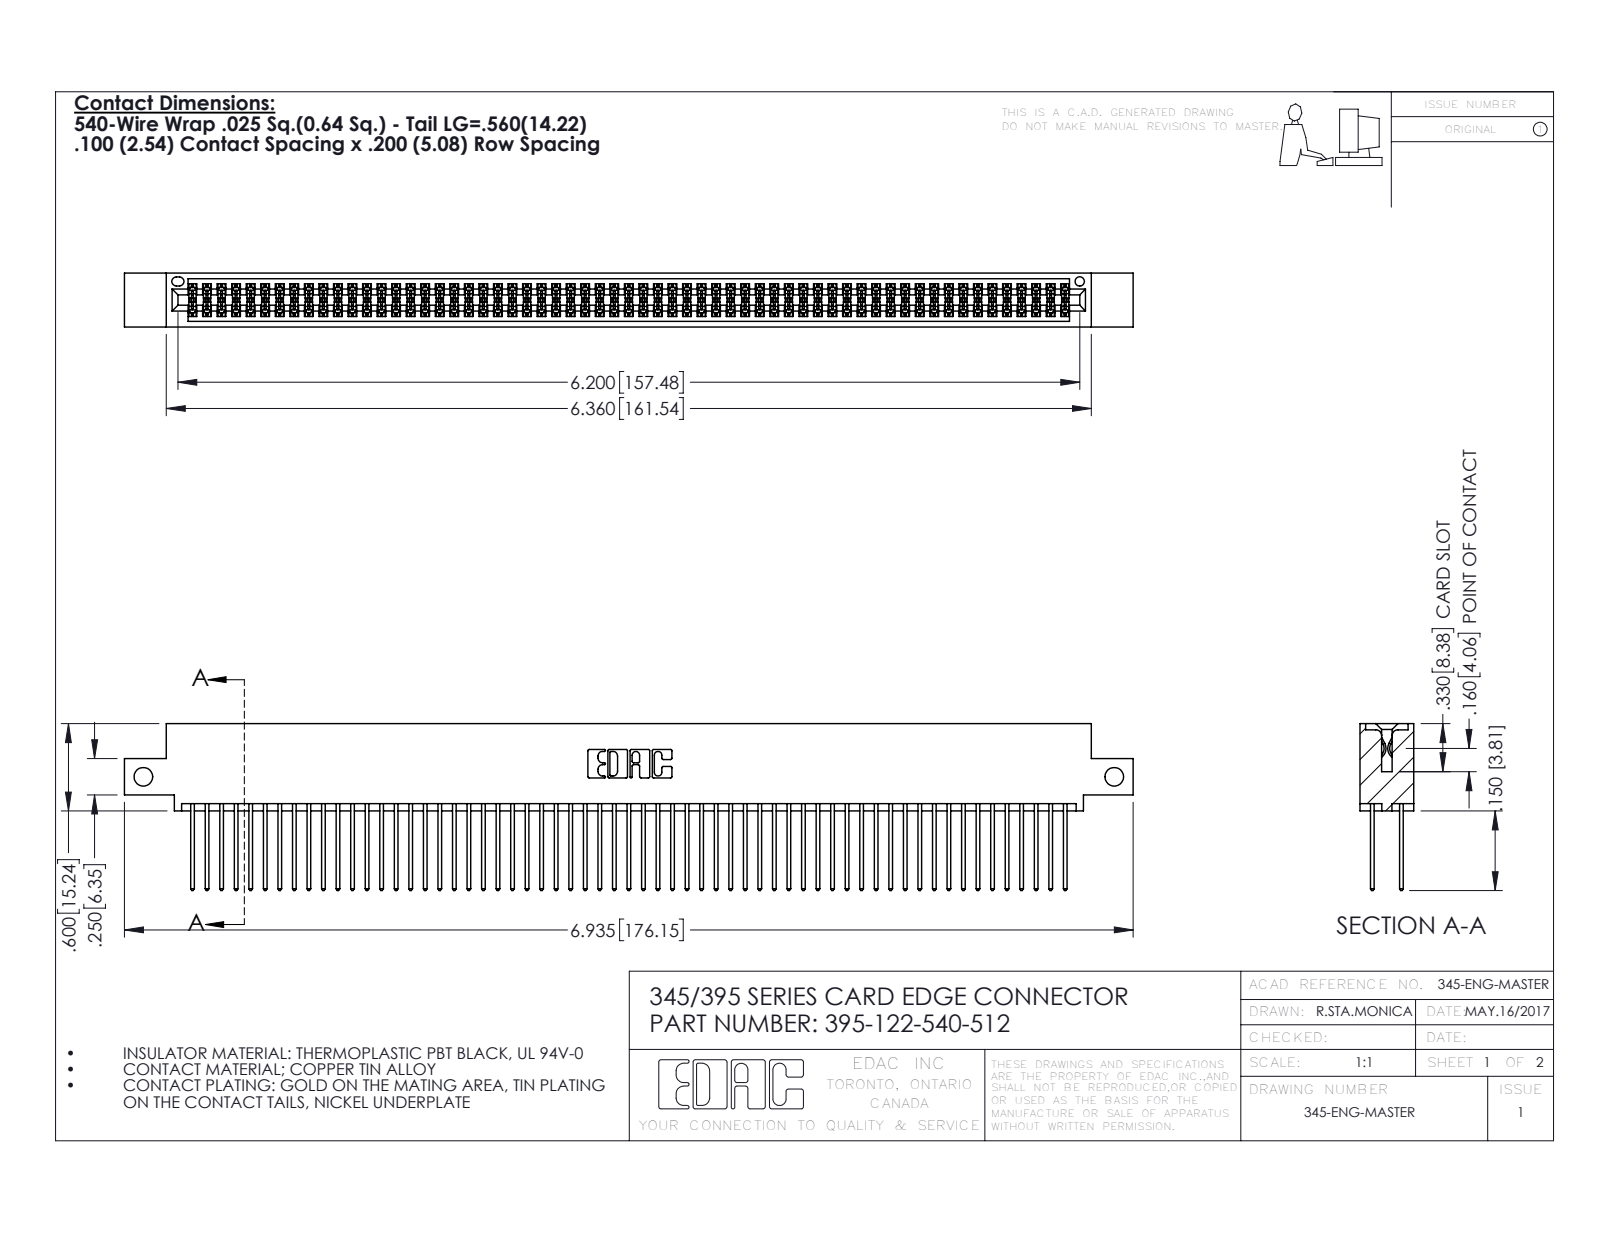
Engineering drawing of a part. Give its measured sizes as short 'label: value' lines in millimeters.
name: 395-122-540-512; 345-292-001_345-293-140; 345 Part_0.110 Offset - Side Mount
written by: SolidWorks 2016 (CONFIG_CONTROL_DESIGN)
unit: mm
bodies: 123 solids, 6230 faces (4110 planar, 2120 cylindrical, 0 other)
size: 176.1 × 29.1 × 9.4
volume: 17 580 mm³; area: 28 470 mm²
holes: 2× ⌀3.3, 1× ⌀1.6
rounds: 183× R0.2, 122× R0.3, 22× R0.3, 6× R0.2, 6× R0.8, 3× R0.7, 2× R0.4, 2× R0.5
face distances: 1.8, 7.6, 5.1, 2.5, 6.9, 0.6, 5.7, 9.4, 4.4, 3.8
hole spacings: 169.5
